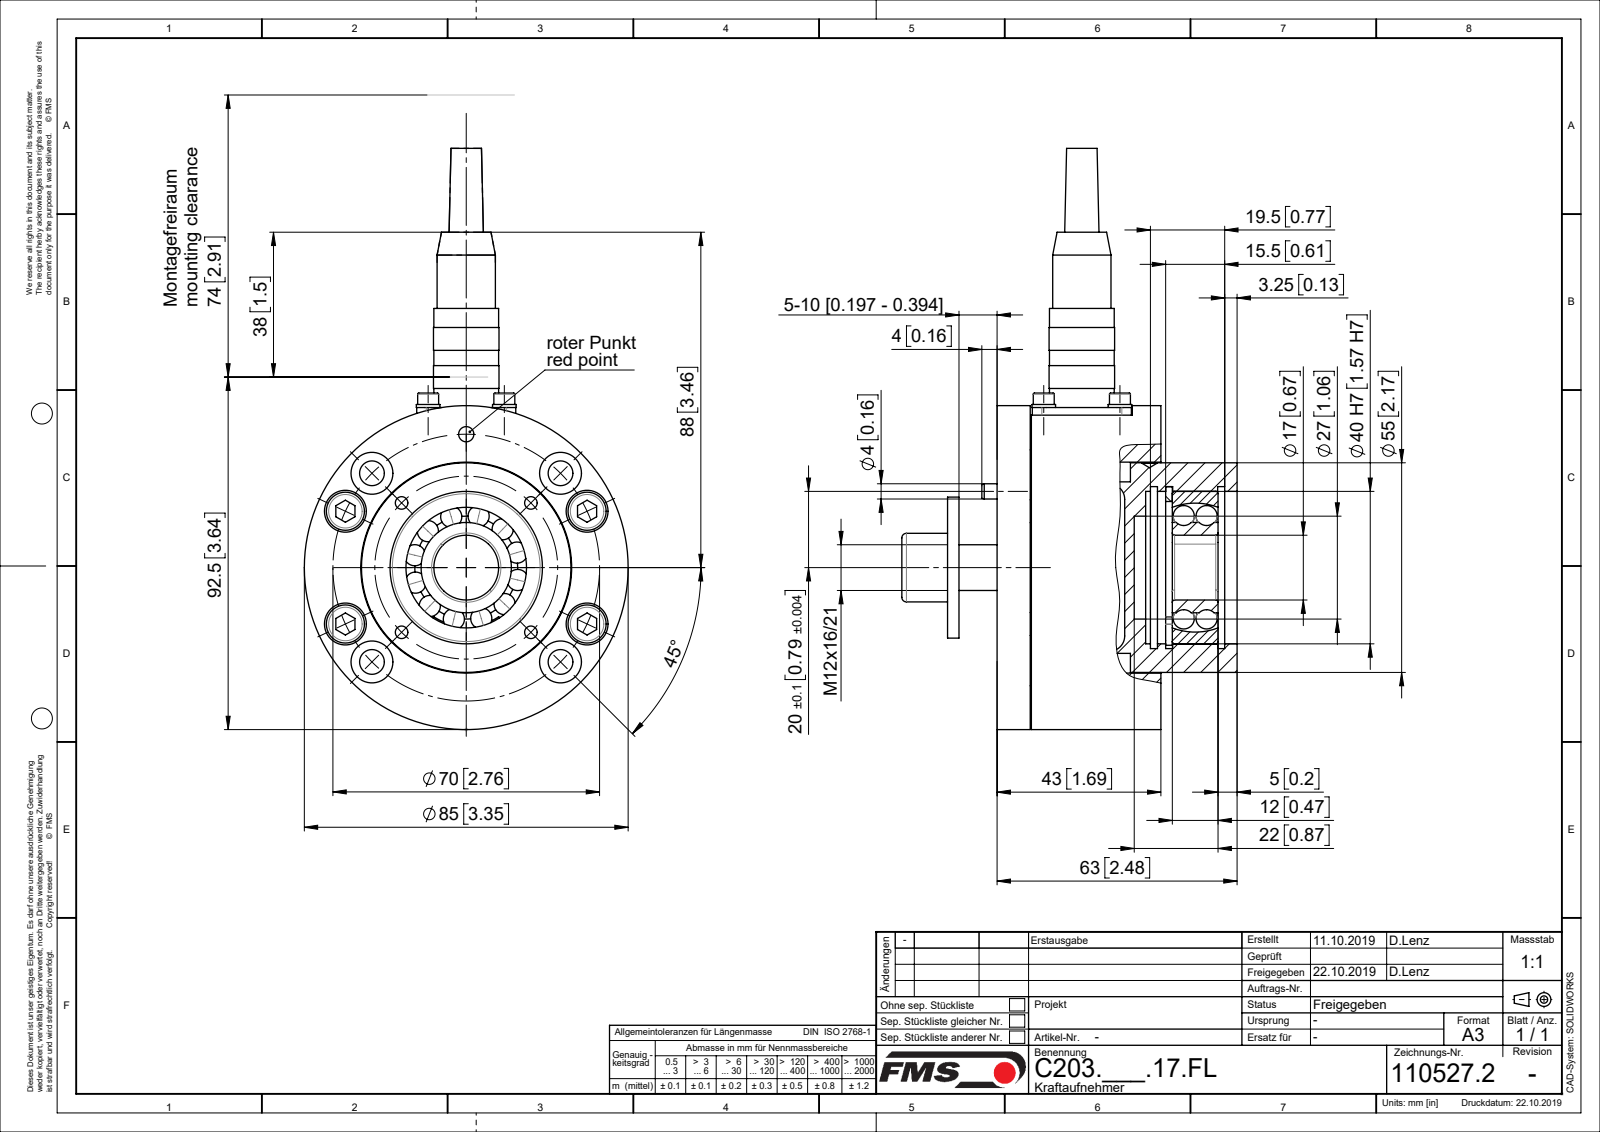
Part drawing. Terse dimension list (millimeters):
name: ZEICHNUNG4; C1105272; C1105271; C0704203 (+8 more)
written by: Mechanical Desktop 2009 (CONFIG_CONTROL_DESIGN)
unit: mm
bodies: 24 solids, 458 faces (141 planar, 235 cylindrical, 82 other)
size: 152.5 × 85 × 67
volume: 252 457 mm³; area: 81 337 mm²
holes: 8× ⌀6.5, 8× ⌀11, 4× ⌀2.6, 4× ⌀3.2, 4× ⌀3.42, 4× ⌀5.15, 4× ⌀7, 1× ⌀4, 1× ⌀10.68, 1× ⌀12, 1× ⌀15, 1× ⌀17
bosses: 5× ⌀1.5, 4× ⌀10, 4× ⌀6.2, 4× ⌀6, 4× ⌀5.5, 4× ⌀5, 4× ⌀3, 1× ⌀85
rounds: 4× R2.5, 2× R5
face distances: 3, 8.7, 34, 42.7, 6, 43, 4, 9, 15, 49
hole spacings: 35, 42.44, 20, 11, 12.16, 14.14, 14.91, 24
